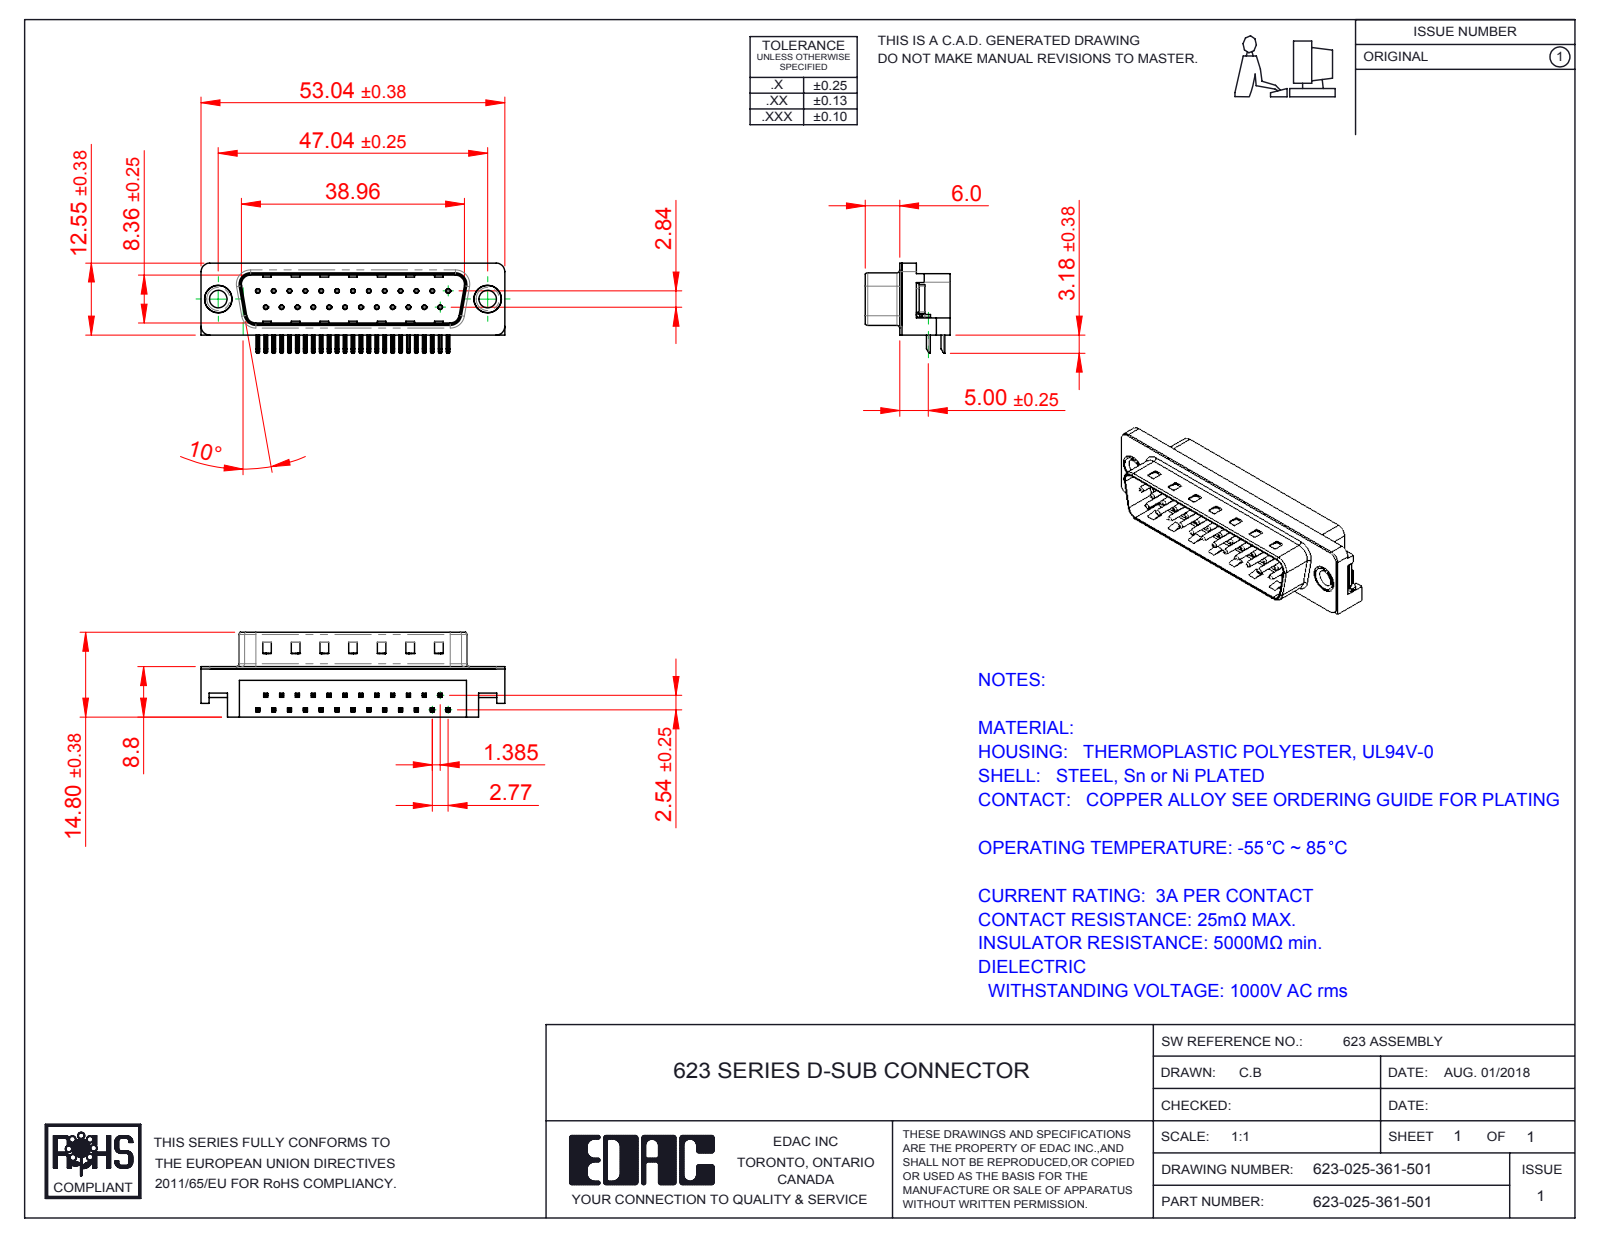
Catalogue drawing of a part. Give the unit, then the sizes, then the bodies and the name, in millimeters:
Units: millimetres
Overall size (bounding box): 53.04 × 15.73 × 14.8
Round holes (diameter × count): ⌀0.35 ×25, ⌀0.8 ×25, ⌀3.05 ×2, ⌀4 ×2, ⌀4.8 ×2, ⌀5 ×2
Round bosses / shafts (diameter × count): ⌀0.75 ×25, ⌀4.9 ×2, ⌀4.75 ×2, ⌀3.85 ×2
Partial cylindrical surfaces — rounded edges, fillets, slot ends (radius × count): R0.25 ×108, R0.12 ×50, R1 ×16, R0.5 ×9, R1.5 ×7, R0.9 ×4, R1.6 ×4, R2 ×4
Main face-to-face distances: 0.4, 8.4, 2.1, 1.7, 8.76, 10.46, 10.86, 10.35, 8.8, 5.9
Hole centre spacings: 3.16, 2.77, 11.08, 5.54, 8.31, 5.03, 13.85, 7.48
Volume: 4 712 mm³ · Surface area: 6 693 mm²
Bodies: 31 solids, 2213 faces (1405 planar, 631 cylindrical, 177 other)
Part name (STEP PRODUCT): 623 Contact Bottom; 623 Housing_25 Socket; 623-025-361-501; 623 Shell_25 Socket (+3 more)
STEP written by: SolidWorks 2016 (CONFIG_CONTROL_DESIGN)
